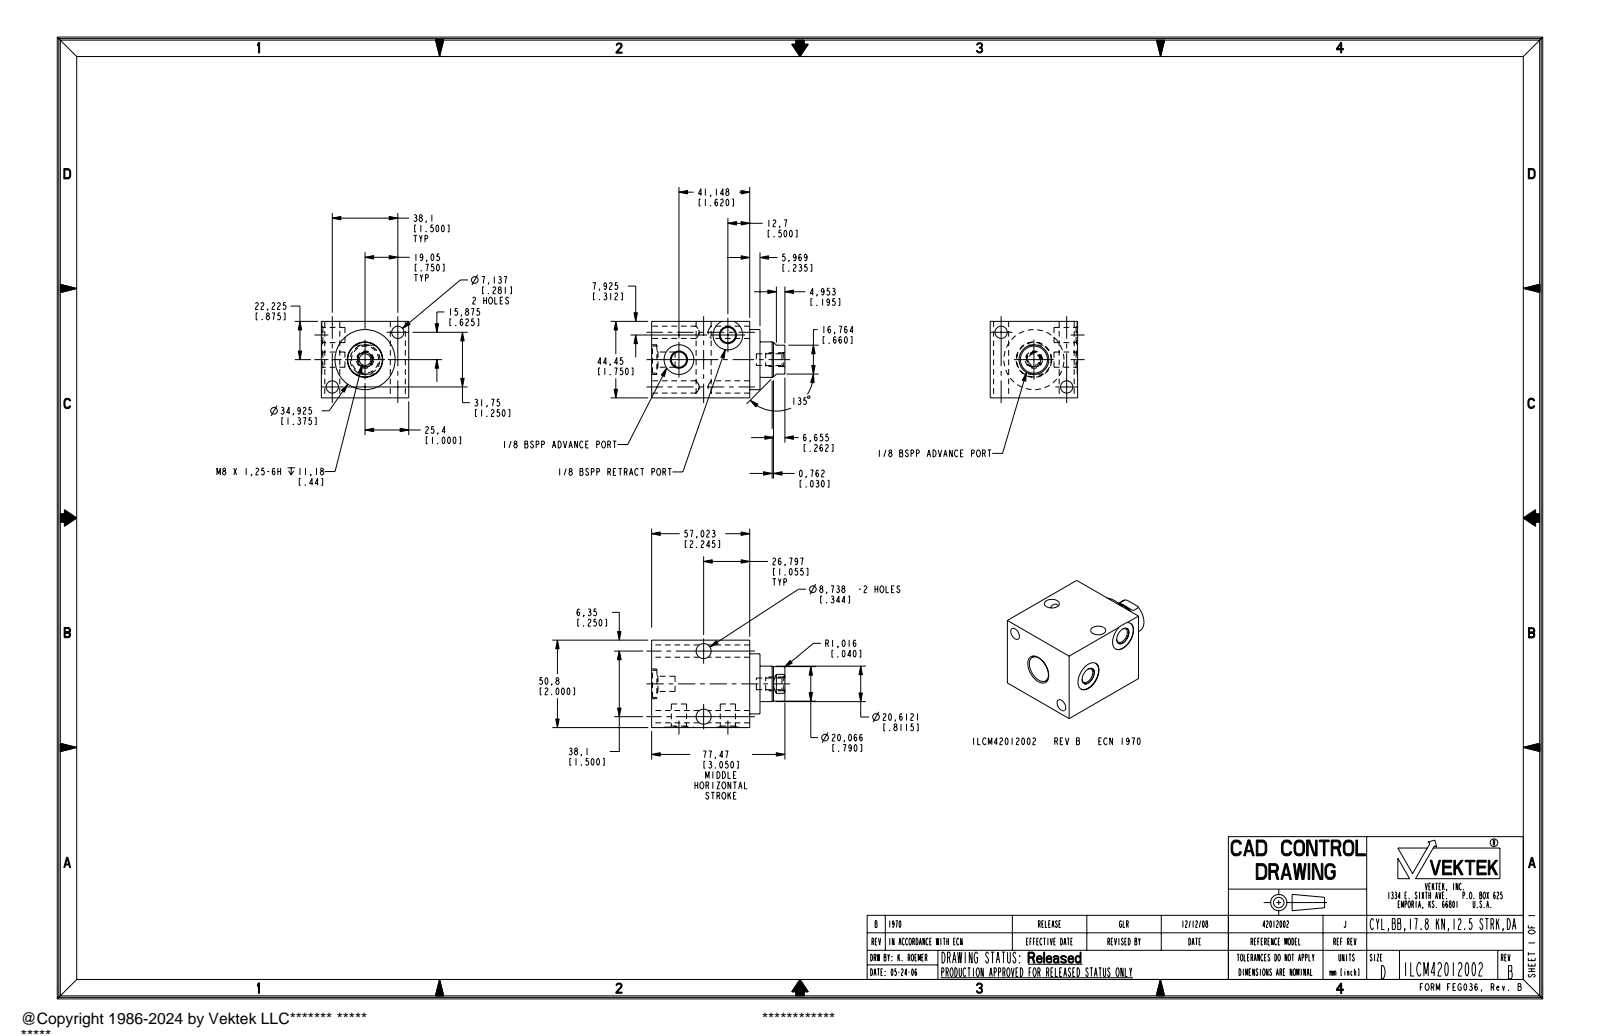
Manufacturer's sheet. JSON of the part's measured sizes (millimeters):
{"part_name": "ILCM42012002", "step_written_by": "PRO/ENGINEER BY PARAMETRIC TECHNOLOGY CORPORATION, 2007460 (AUTOMOTIVE_DESIGN_CC2)", "units": "millimeters", "bodies": {"solids": 1, "faces": 75, "planar": 22, "cylindrical": 41, "other": 12}, "overall_size": [77.47, 50.8, 44.45], "volume_mm3": 126507, "surface_area_mm2": 23115, "round_holes": [[8.84, 3], [10.03, 3], [17.27, 3], [7.14, 2], [8.74, 2], [6.78, 1]], "round_bosses_or_shafts": [[34.92, 1], [20.61, 1], [20.07, 1], [15.75, 1], [8, 1]], "face_to_face_distances": [44.46, 50.8, 57.02, 5.97, 62.99, 50.55, 62.49, 56.52, 0.5, 14.48], "hole_center_spacings": [24.8, 31.84, 38.1, 49.6]}
